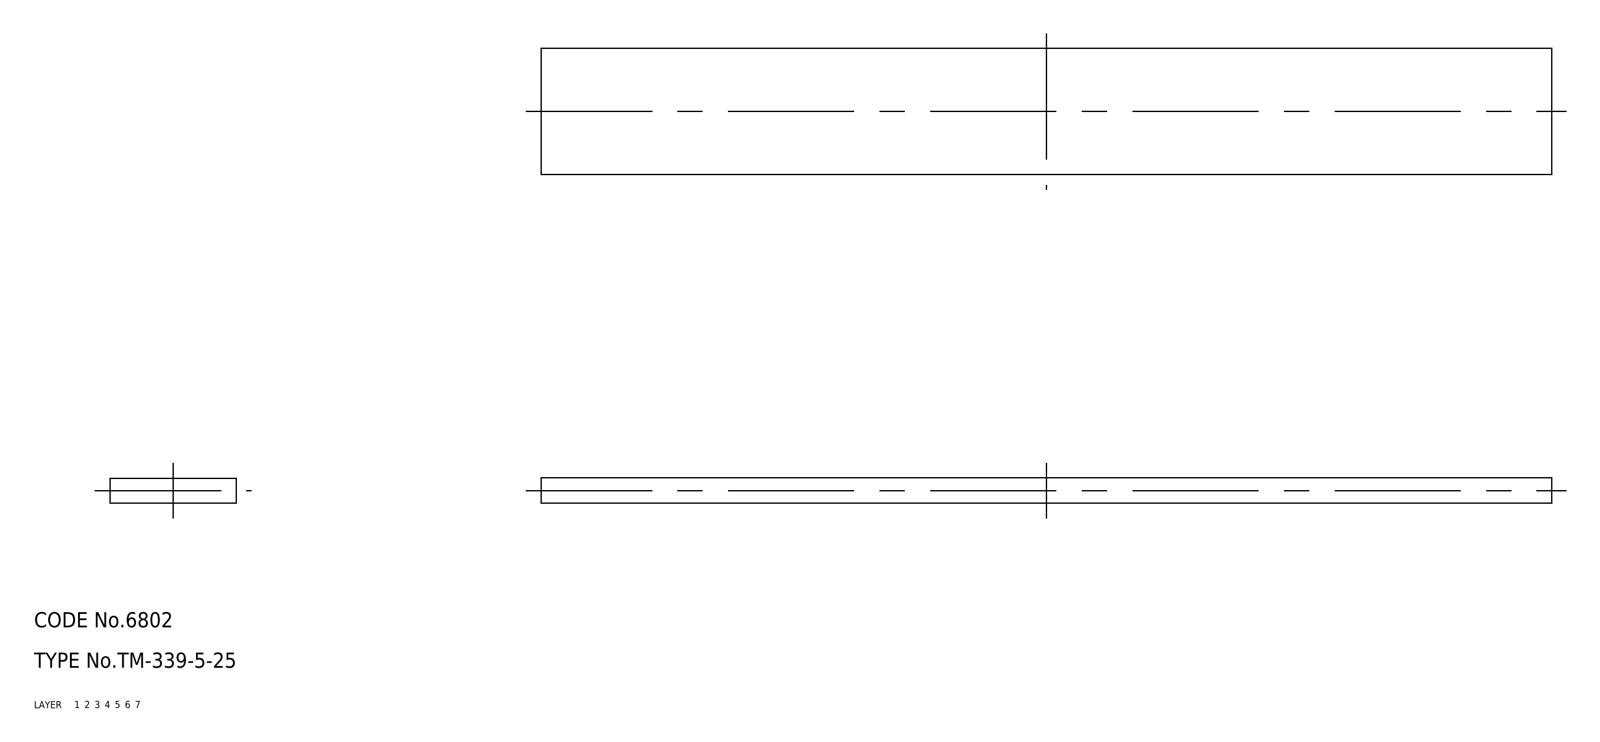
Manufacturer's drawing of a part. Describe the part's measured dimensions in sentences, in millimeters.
The part is named "rubber foam; TM_339_5_25". Its 3-D file was written by "SolidWorks 2015 (AUTOMOTIVE_DESIGN)". It is 1 solid with 6 faces: 6 planar, 0 cylindrical and 0 other. Overall it measures 200 by 25 by 5 millimeters. Its volume is 25 000 cubic millimeters and its surface area 12 250 square millimeters. The main face-to-face distances are 5, 25, 200.
